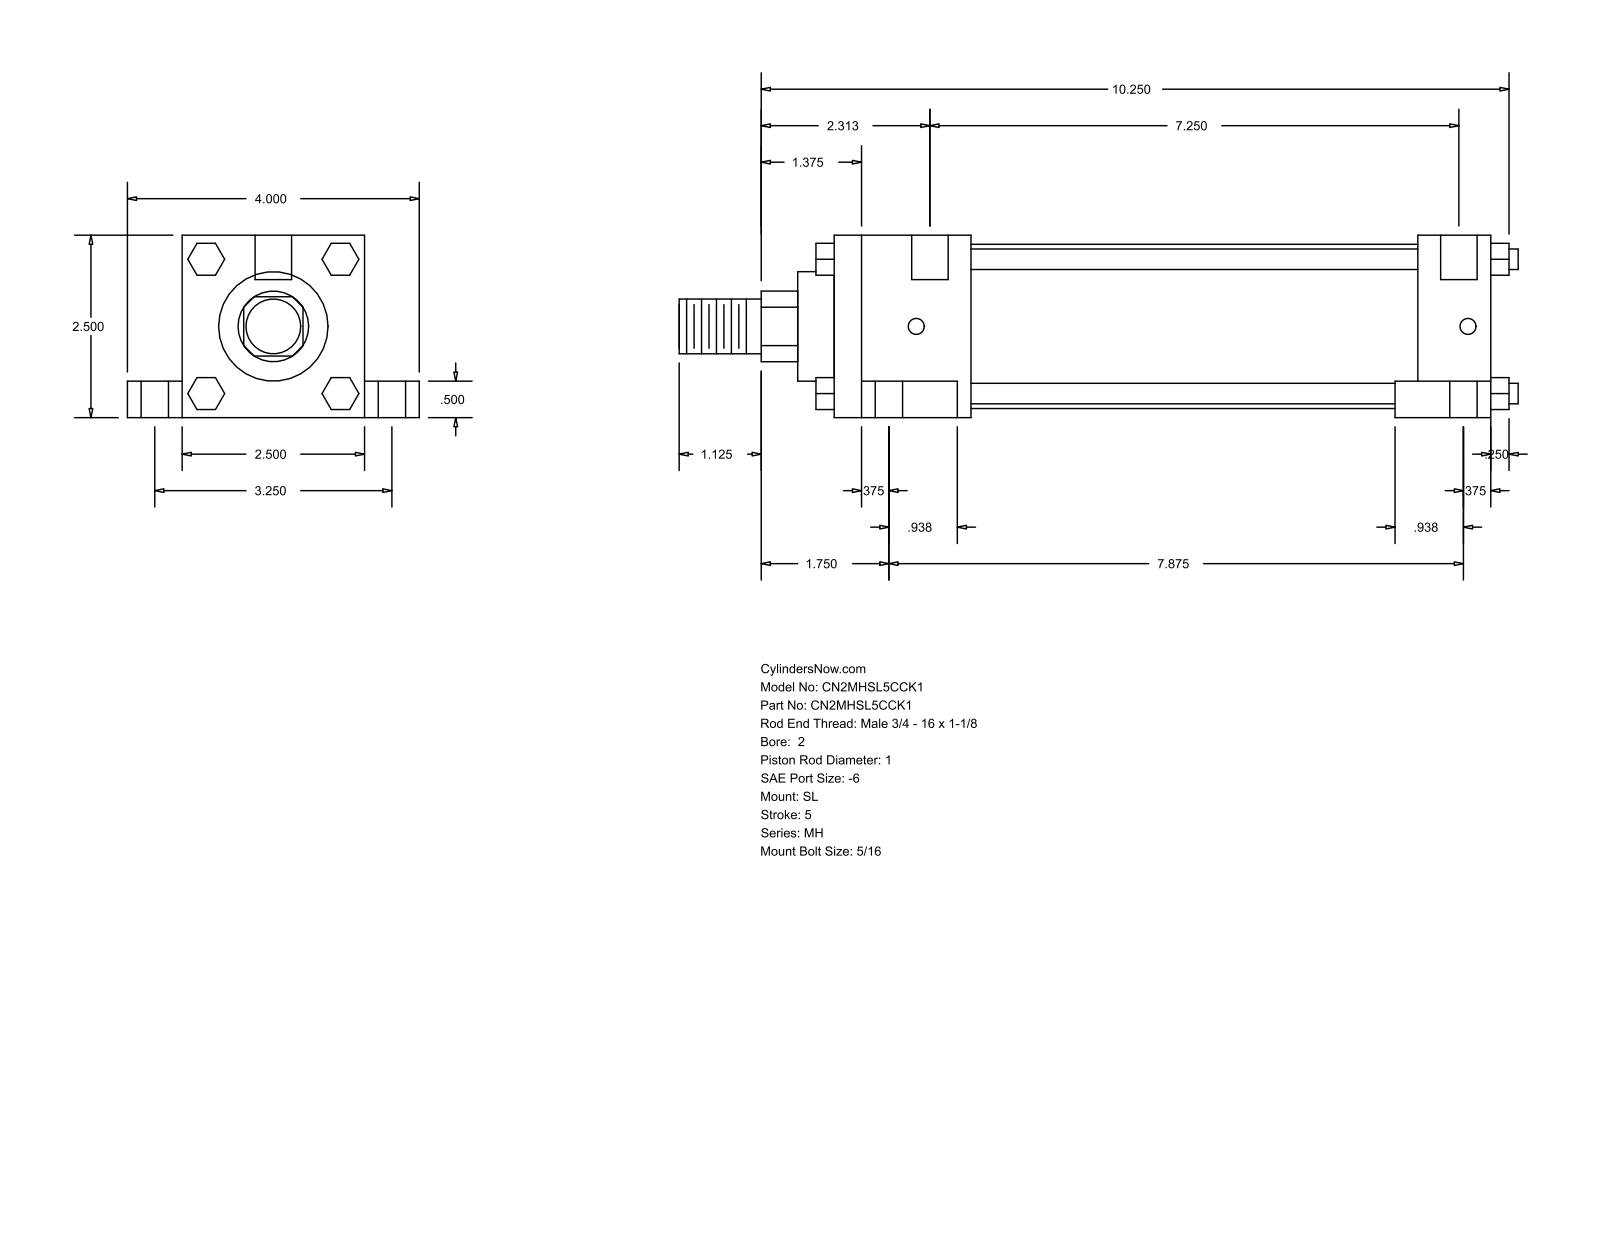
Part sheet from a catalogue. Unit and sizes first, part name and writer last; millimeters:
Units: millimetres
Overall size (bounding box): 292.1 × 101.6 × 63.5
Round holes (diameter × count): ⌀5.56 ×4, ⌀9.53 ×4, ⌀15.88 ×4, ⌀12.7 ×2
Round bosses / shafts (diameter × count): ⌀7.14 ×4, ⌀57.15 ×1, ⌀38.1 ×1, ⌀25.4 ×1, ⌀19.05 ×1
Partial cylindrical surfaces — rounded edges, fillets, slot ends (radius × count): R12.29 ×1
Main face-to-face distances: 63.5, 228.6, 12.7, 19.05, 50.8, 82.55, 25.4, 203.2, 47.63, 155.57
Hole centre spacings: 41.3, 42.36, 43.67, 82.54, 190.26, 192.08, 194.91, 200.02
Bodies: 0 solids, 148 faces (112 planar, 36 cylindrical, 0 other)
Part name (STEP PRODUCT): MH_SL__0200_1
STEP written by: GSSL Pune (CONFIG_CONTROL_DESIGN)
